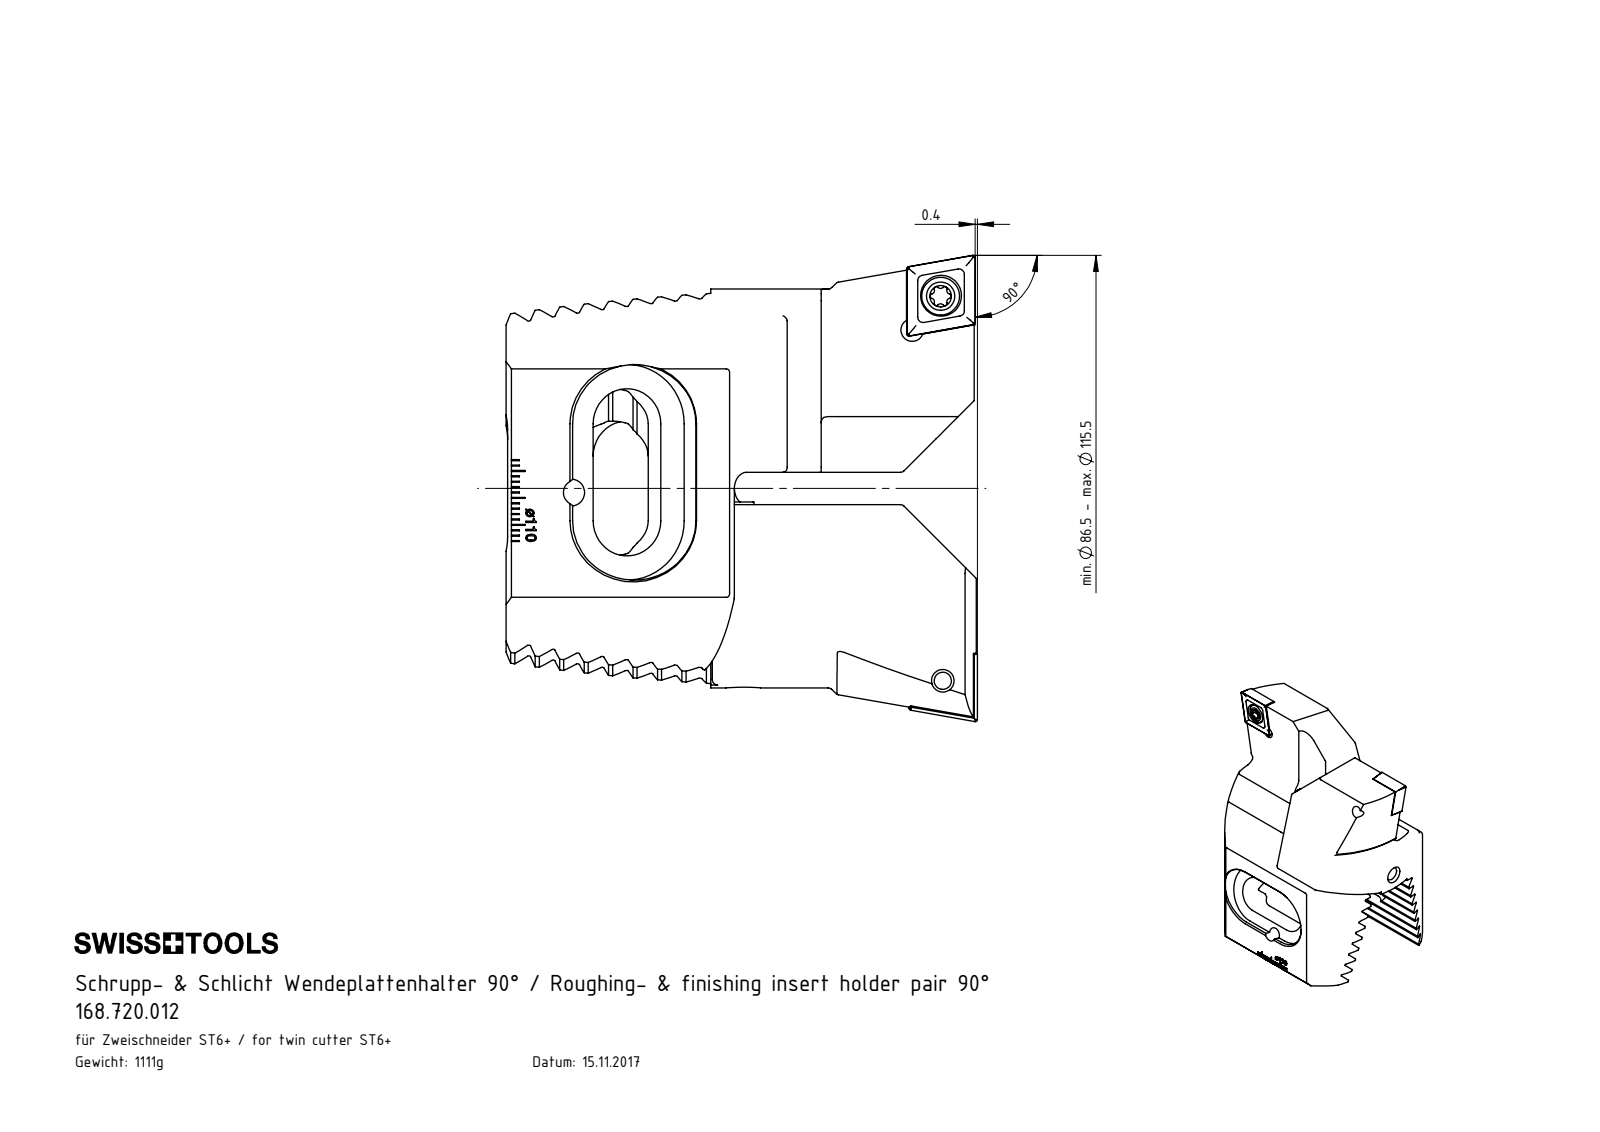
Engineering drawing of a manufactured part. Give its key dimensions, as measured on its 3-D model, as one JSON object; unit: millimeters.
{"part_name": "ZC7-xxx.001.050_A_versetzt Combi; ZC7-xxx.001.050_A; 168.720.012; Z72-ER3.001.030 (+3 more)", "step_written_by": "SolidWorks 2017 (CONFIG_CONTROL_DESIGN)", "units": "millimeters", "bodies": {"solids": 8, "faces": 746, "planar": 411, "cylindrical": 143, "other": 192}, "overall_size": [87.5, 86.5, 58.2], "volume_mm3": 142276, "surface_area_mm2": 37228, "round_holes": [[4.2, 4], [5, 2], [5.5, 2], [7.6, 2], [2, 1], [2.5, 1], [8, 1]], "round_bosses_or_shafts": [[7, 2], [5, 2], [6, 1], [4, 1], [3, 1], [2, 1]], "partial_cylinders_radius": [[0.34, 16], [1, 16], [0.39, 12], [0.69, 6], [0.69, 6], [3, 4], [6.5, 4], [11, 4]], "face_to_face_distances": [4.07, 8.14, 20.36, 12.21, 28.8, 29.4, 58.2, 16.29, 20.34, 24.43], "hole_center_spacings": [8.21, 8.33, 71.43, 20, 58.76, 65.23, 65.3, 65.33]}
